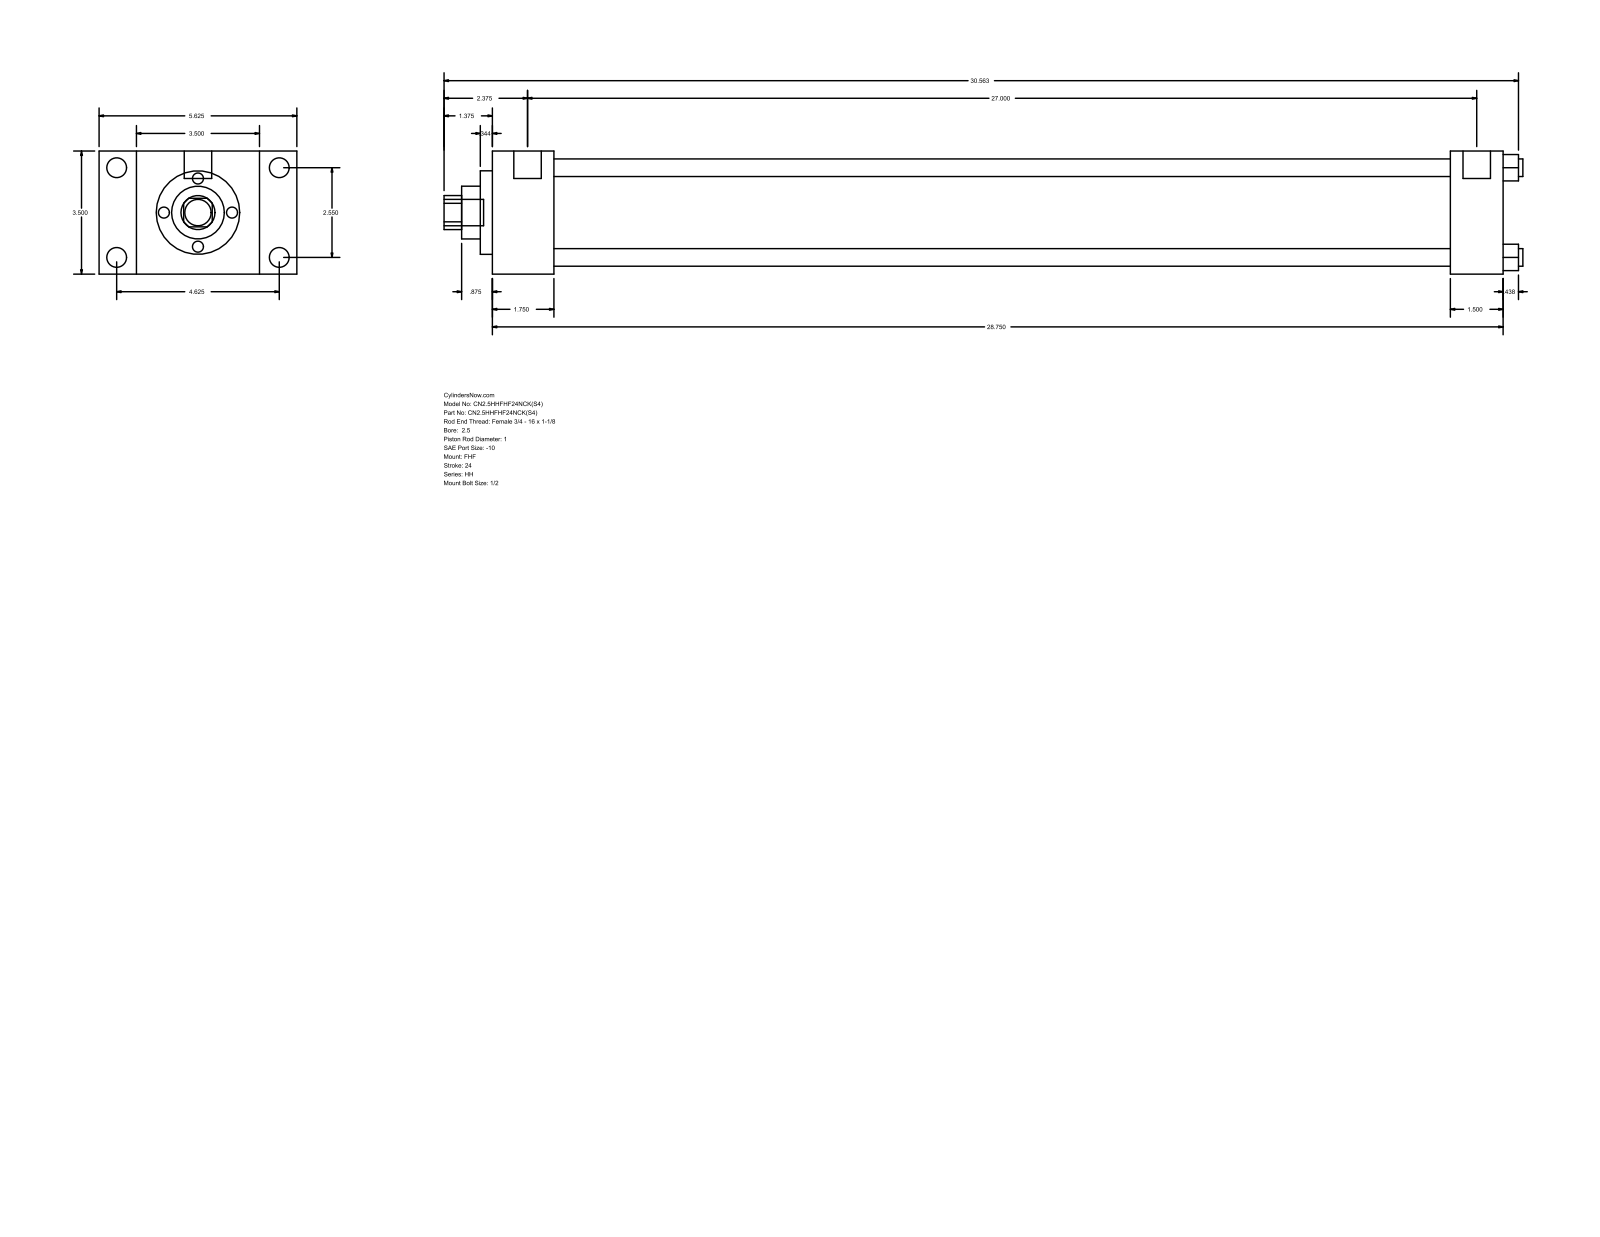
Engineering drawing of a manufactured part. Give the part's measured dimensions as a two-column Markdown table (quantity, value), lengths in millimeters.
| quantity | value |
| --- | --- |
| part name | HH_FHF__0250_1 |
| STEP written by | GSSL Pune (CONFIG_CONTROL_DESIGN) |
| units | millimeters |
| bodies | 0 solids, 90 faces (61 planar, 29 cylindrical, 0 other) |
| overall size | 779.46 × 142.88 × 88.9 |
| round holes (diameter × count) | 12.7 × 4, 25.4 × 1, 38.1 × 1, 60.33 × 1, 73.03 × 1 |
| round bosses / shafts (diameter × count) | 14.3 × 4, 5.56 × 4, 19.84 × 2, 19.05 × 1 |
| partial cylindrical surfaces (radius × count) | 12.29 × 1 |
| main face-to-face distances | 88.9, 44.46, 26.99, 115.89, 730.25, 685.79, 142.88, 692.16, 647.7, 38.09 |
| hole center spacings | 45.79, 64.76, 91.58 |
